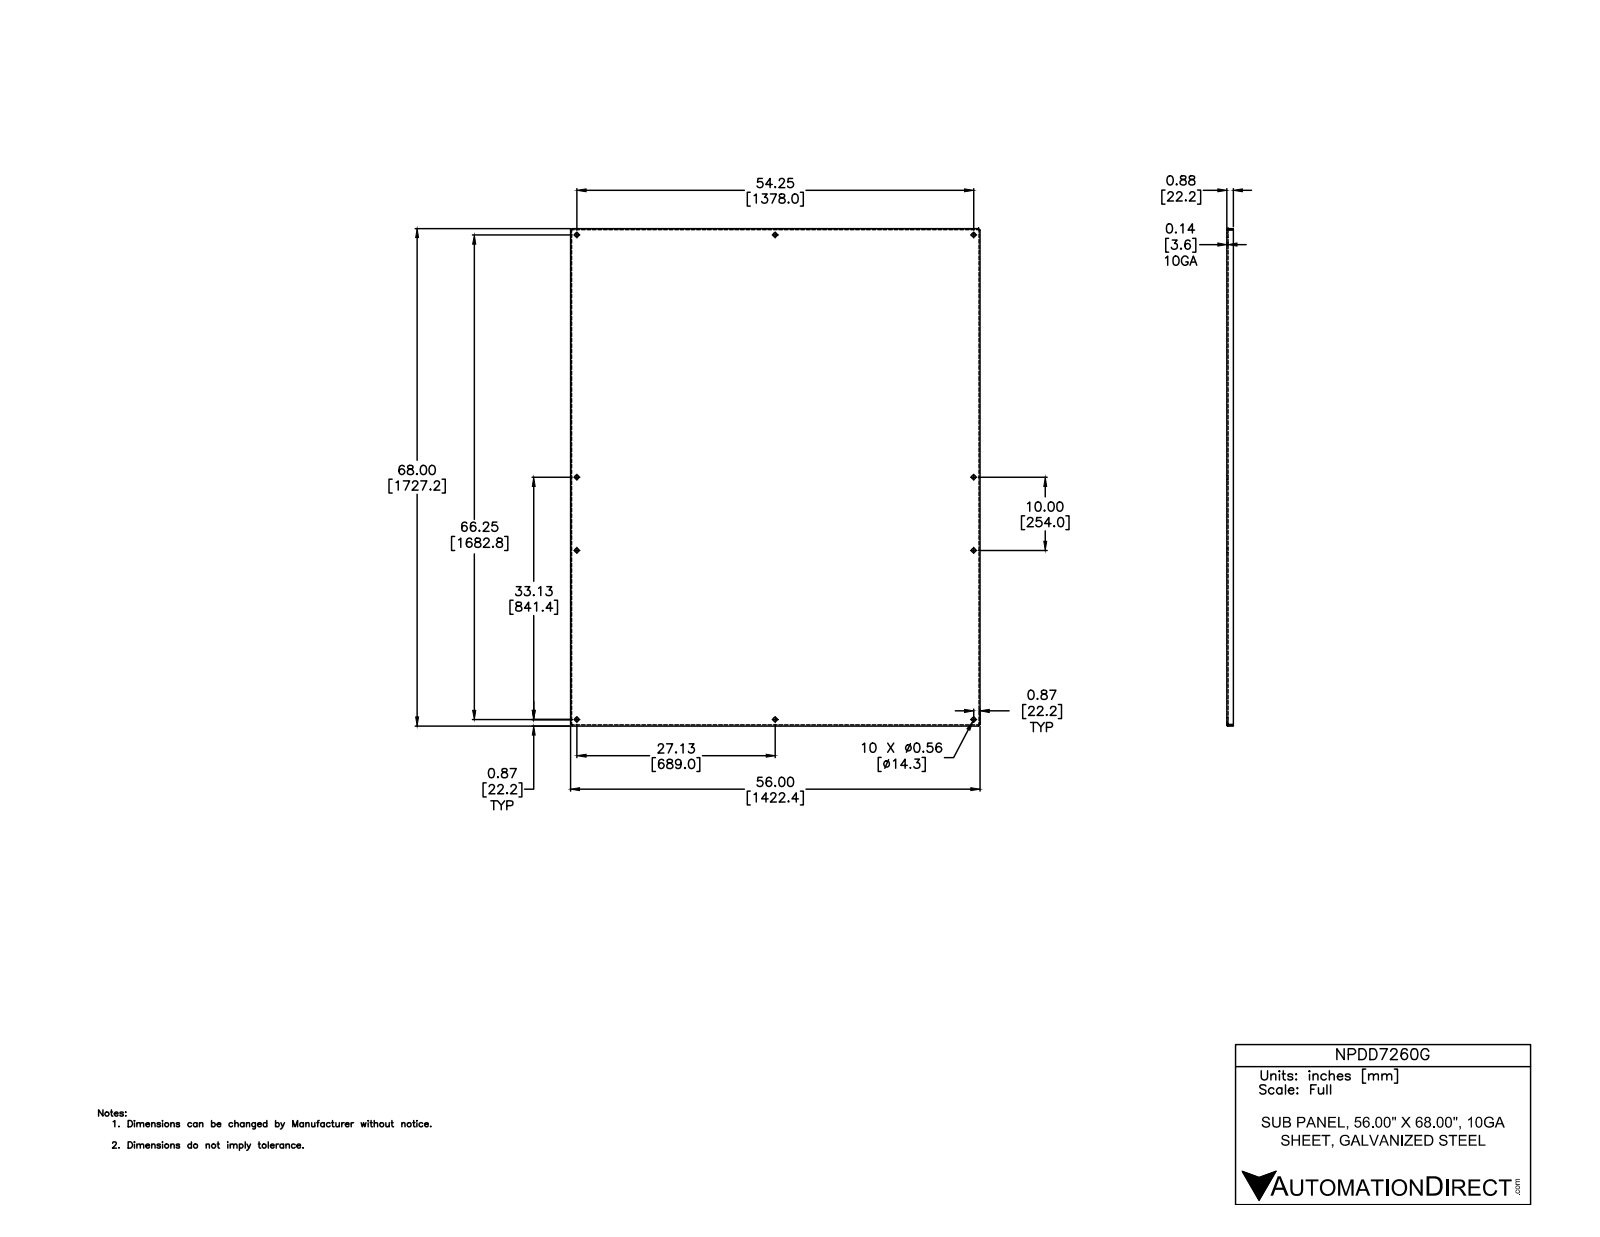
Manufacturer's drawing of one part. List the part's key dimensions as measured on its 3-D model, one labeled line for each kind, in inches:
Part name (STEP PRODUCT): NPDD4242G-NPDD7272G
STEP written by: Autodesk Inventor 2012 (AUTOMOTIVE_DESIGN)
Units: inches
Bodies: 1 solid, 48 faces (22 planar, 18 cylindrical, 8 other)
Overall size (bounding box): 68 × 56 × 0.875
Volume: 497.5 in³ · Surface area: 7 994 in²
Round holes (diameter × count): ⌀0.563 ×10
Partial cylindrical surfaces — rounded edges, fillets, slot ends (radius × count): R0.031 ×4, R0.156 ×4
Main face-to-face distances: 0.125, 0.125, 56, 55.875, 55.875, 55.75, 67.875, 68, 67.75, 67.875
Hole centre spacings: 27.125, 42.814, 54.25, 33.125, 63.564, 71.588, 10, 35.645
